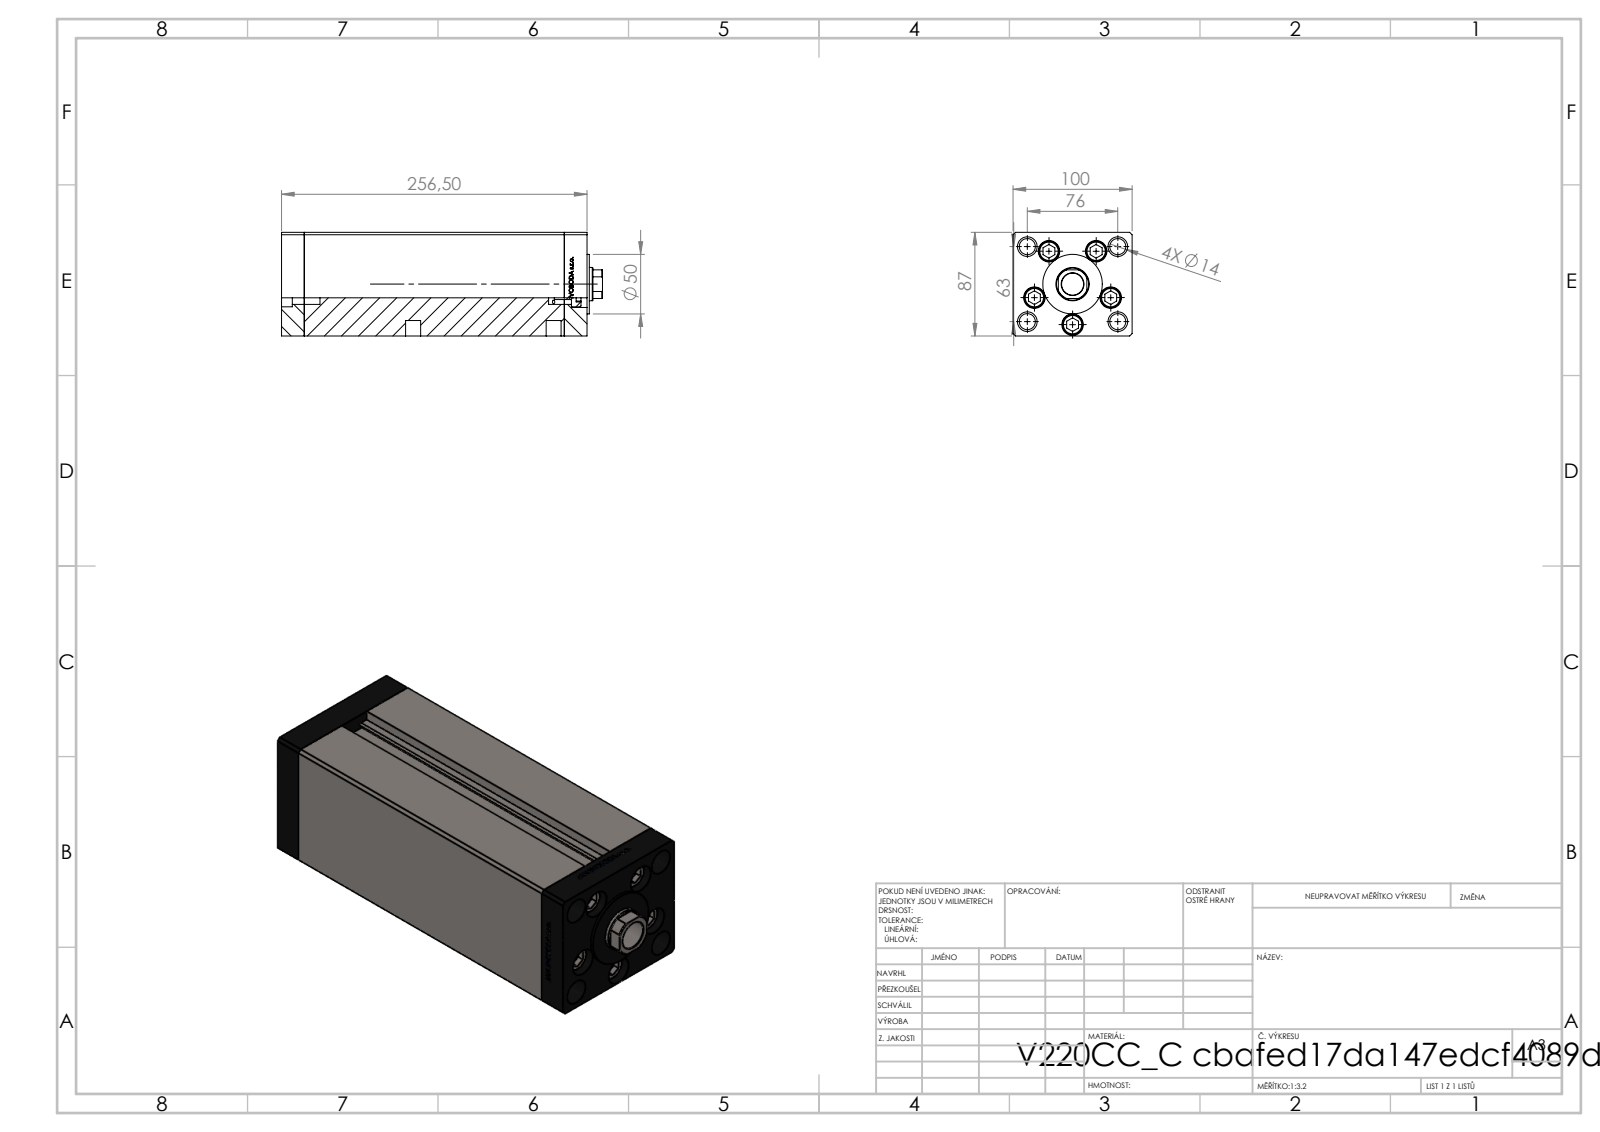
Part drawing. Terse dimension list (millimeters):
name: V220C_VC_C; ALLEN BOLT; V220C FRONT; V220C BACK_C (+1 more)
written by: SolidWorks 2019 (CONFIG_CONTROL_DESIGN)
unit: mm
bodies: 13 solids, 1186 faces (548 planar, 176 cylindrical, 462 other)
size: 269.5 × 100 × 87
volume: 1 820 000 mm³; area: 279 473 mm²
holes: 9× ⌀13.5, 5× ⌀18, 4× ⌀2, 4× ⌀12, 4× ⌀13.16, 4× ⌀16.5, 1× ⌀17, 1× ⌀18.5, 1× ⌀28
bosses: 5× ⌀8, 4× ⌀17, 1× ⌀50
rounds: 2× R0.93, 1× R13.5
face distances: 100, 87, 19, 218.5, 237.5, 34.25, 256.5, 222.25, 203.25, 15.25
hole spacings: 34, 49.36, 18.59, 21.03, 38.08, 39.27, 40.83, 43.24
